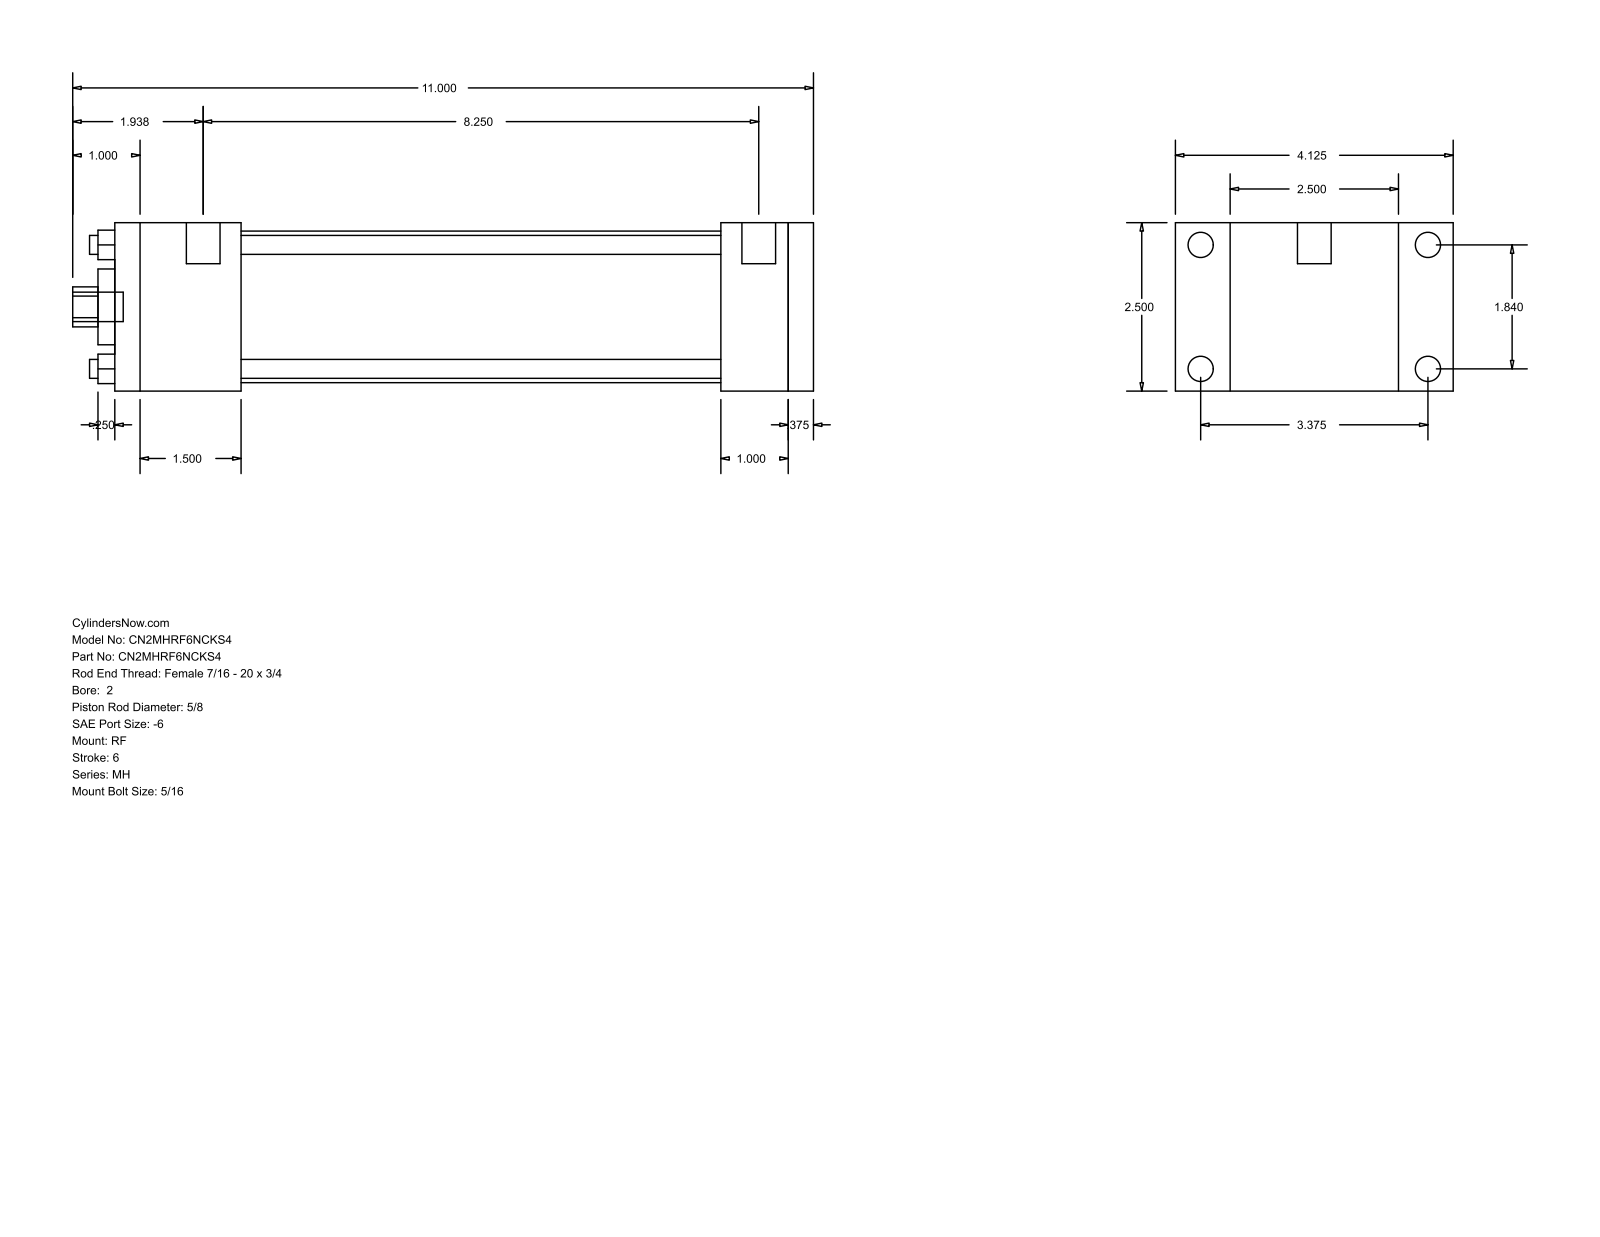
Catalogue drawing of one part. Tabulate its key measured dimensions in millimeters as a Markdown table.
| quantity | value |
| --- | --- |
| part name | MH_RF__0200_0.625 |
| STEP written by | GSSL Pune (CONFIG_CONTROL_DESIGN) |
| units | millimeters |
| bodies | 0 solids, 92 faces (64 planar, 28 cylindrical, 0 other) |
| overall size | 279.4 × 104.78 × 63.5 |
| round holes (diameter × count) | 7.14 × 4, 15.88 × 1, 28.57 × 1, 57.15 × 1 |
| round bosses / shafts (diameter × count) | 9.53 × 4, 5.56 × 4, 12.7 × 2, 11.11 × 1 |
| partial cylindrical surfaces (radius × count) | 7.54 × 1 |
| main face-to-face distances | 63.5, 263.52, 9.52, 254, 47.62, 228.59, 180.97, 206.38, 215.9, 25.41 |
| hole center spacings | 33.05, 46.74, 66.1 |
